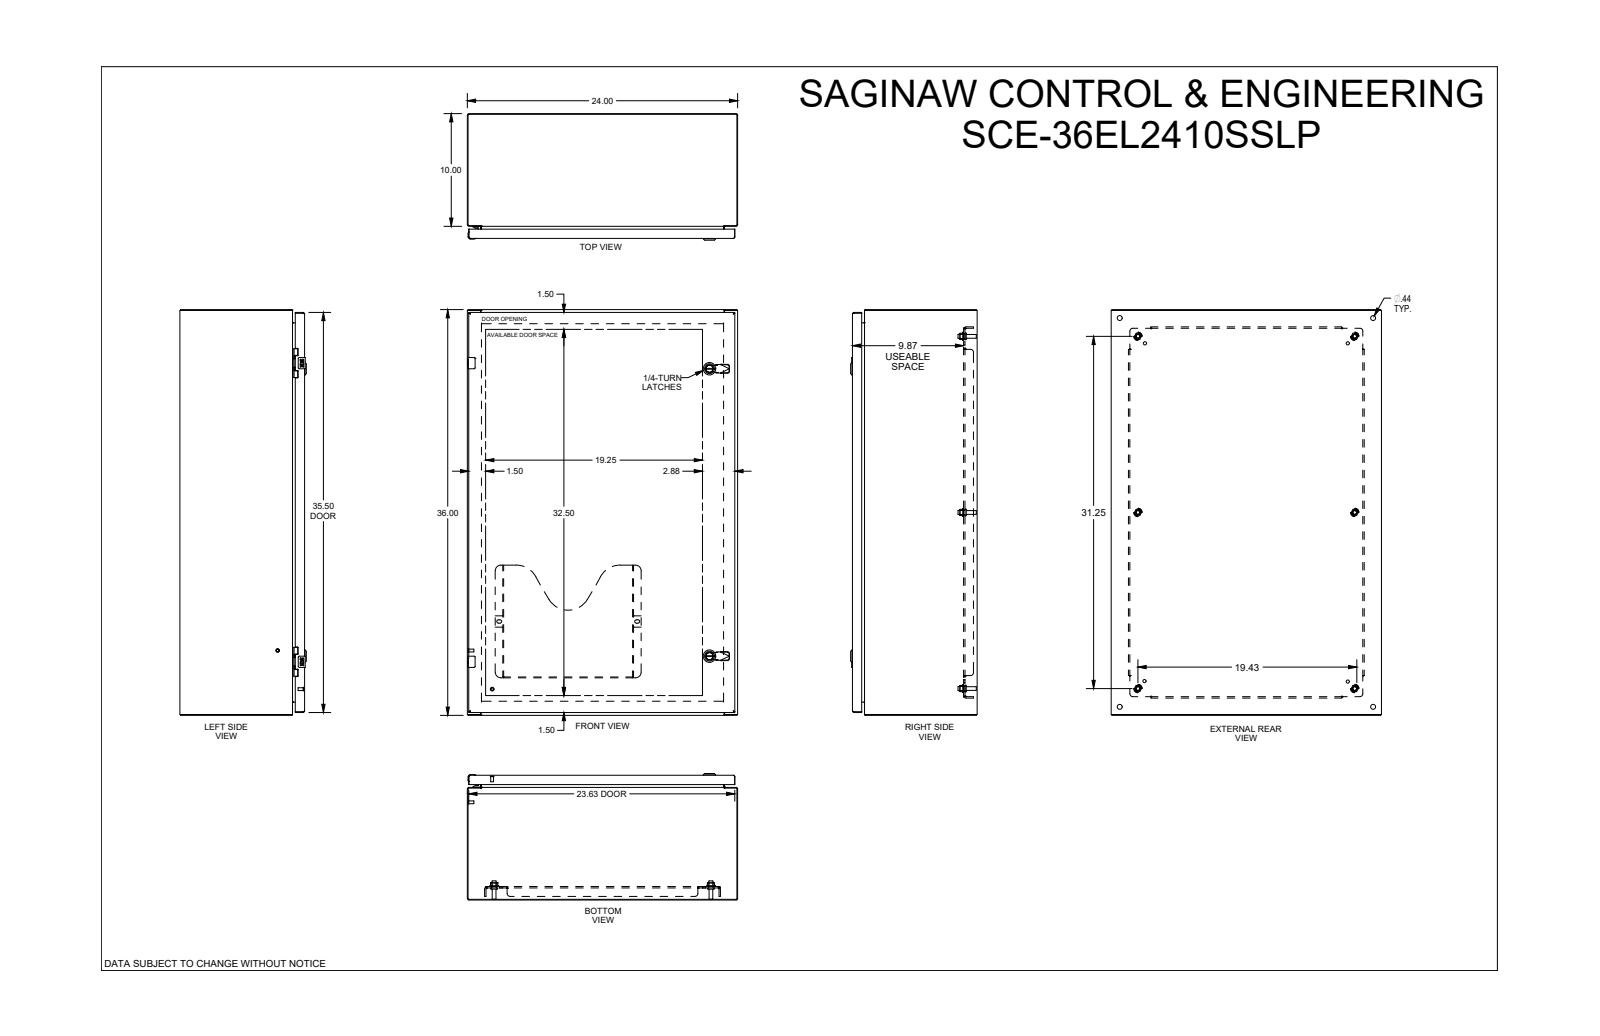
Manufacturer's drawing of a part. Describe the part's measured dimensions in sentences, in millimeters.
The part is named "SCE-36EL2410SSLP". Its 3-D file was written by "SolidWorks 2019 (CONFIG_CONTROL_DESIGN)". It is 0 solids with 2948 faces: 1331 planar, 779 cylindrical and 838 other. Overall it measures 914.4 by 609.6 by 285.2 millimeters. Round holes: 6 of diameter 9.3, 6 of diameter 12.7, 4 of diameter 4.4, 4 of diameter 5.2, 4 of diameter 6.2, 4 of diameter 6.8, 4 of diameter 7.1, 4 of diameter 9.5, 4 of diameter 11.1, 2 of diameter 4, 2 of diameter 5, 2 of diameter 5.5. Round bosses or shafts: 6 of diameter 9.3, 6 of diameter 8.4, 6 of diameter 4.3, 4 of diameter 6.4, 4 of diameter 6.3, 3 of diameter 5, 2 of diameter 28, 2 of diameter 22. Partial cylindrical surfaces (rounded edges, fillets, slot ends): 56 of radius 0.3, 40 of radius 0.3, 32 of radius 0.4, 23 of radius 1, 20 of radius 0.5, 12 of radius 0.7, 10 of radius 1.8, 10 of radius 3.7. The main face-to-face distances are 1.9, 1.9, 277.4, 279.3, 281.3, 279.3, 30.5, 250.8, 607.7, 25.4. The hole center spacings are 673.1, 25, 0.5, 58.4, 114.1, 396.9, 440.1, 531.8.
